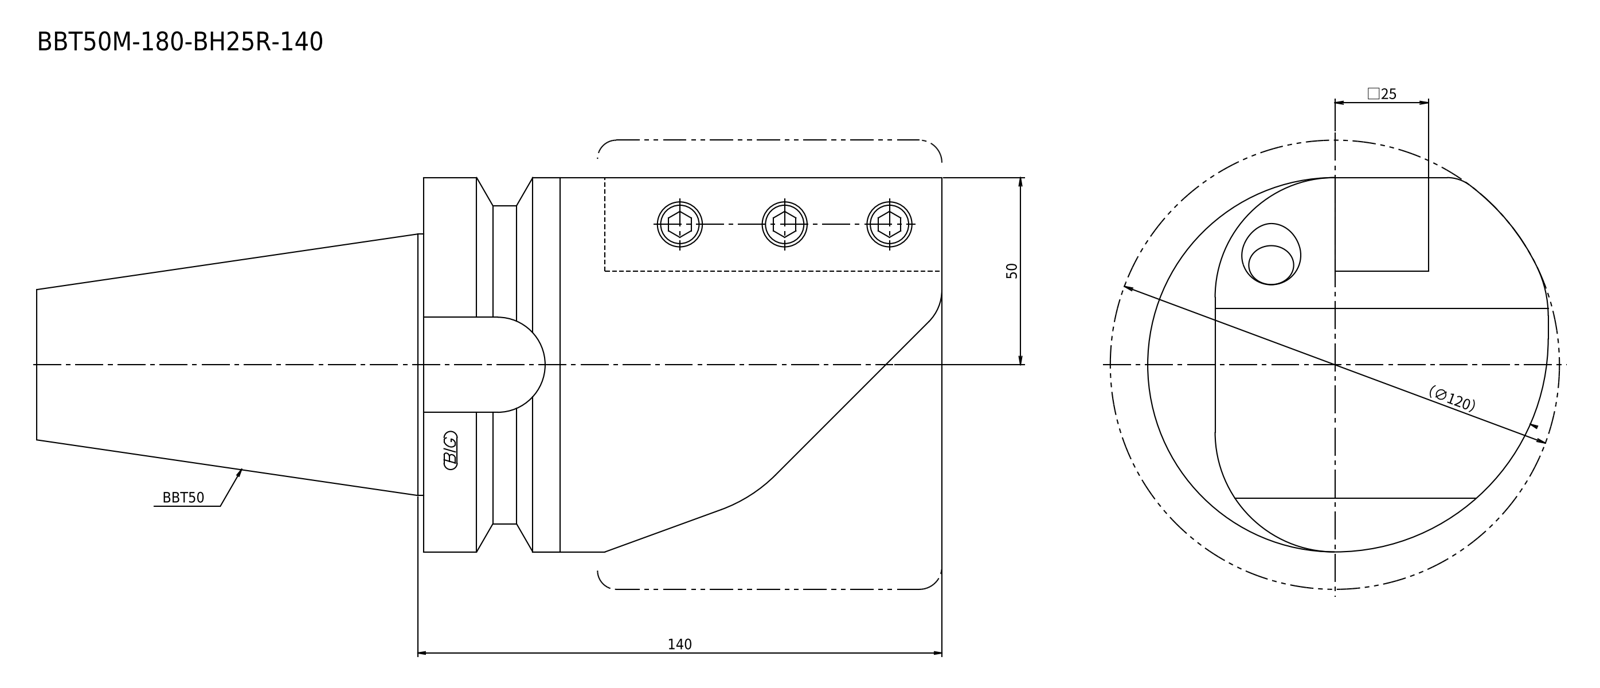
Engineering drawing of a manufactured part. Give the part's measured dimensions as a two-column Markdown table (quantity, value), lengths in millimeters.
| quantity | value |
| --- | --- |
| STEP written by | Kubotek KeyCreator 2011 V10.0.2 (22737) (automotive_design) |
| units | millimeters |
| bodies | 1 solid, 25 faces (14 planar, 8 cylindrical, 3 other) |
| overall size | 241.8 × 107 × 100 |
| volume | 1 070 000 mm³ |
| surface area | 76 918 mm² |
| round bosses / shafts (diameter × count) | 100 × 1, 85 × 1, 69.85 × 1 |
| partial cylindrical surfaces (radius × count) | 32 × 2, 57 × 1, 60 × 1 |
| main face-to-face distances | 32, 57, 25, 138.5, 241.8, 103.3, 102, 36.5, 139.8, 89 |
